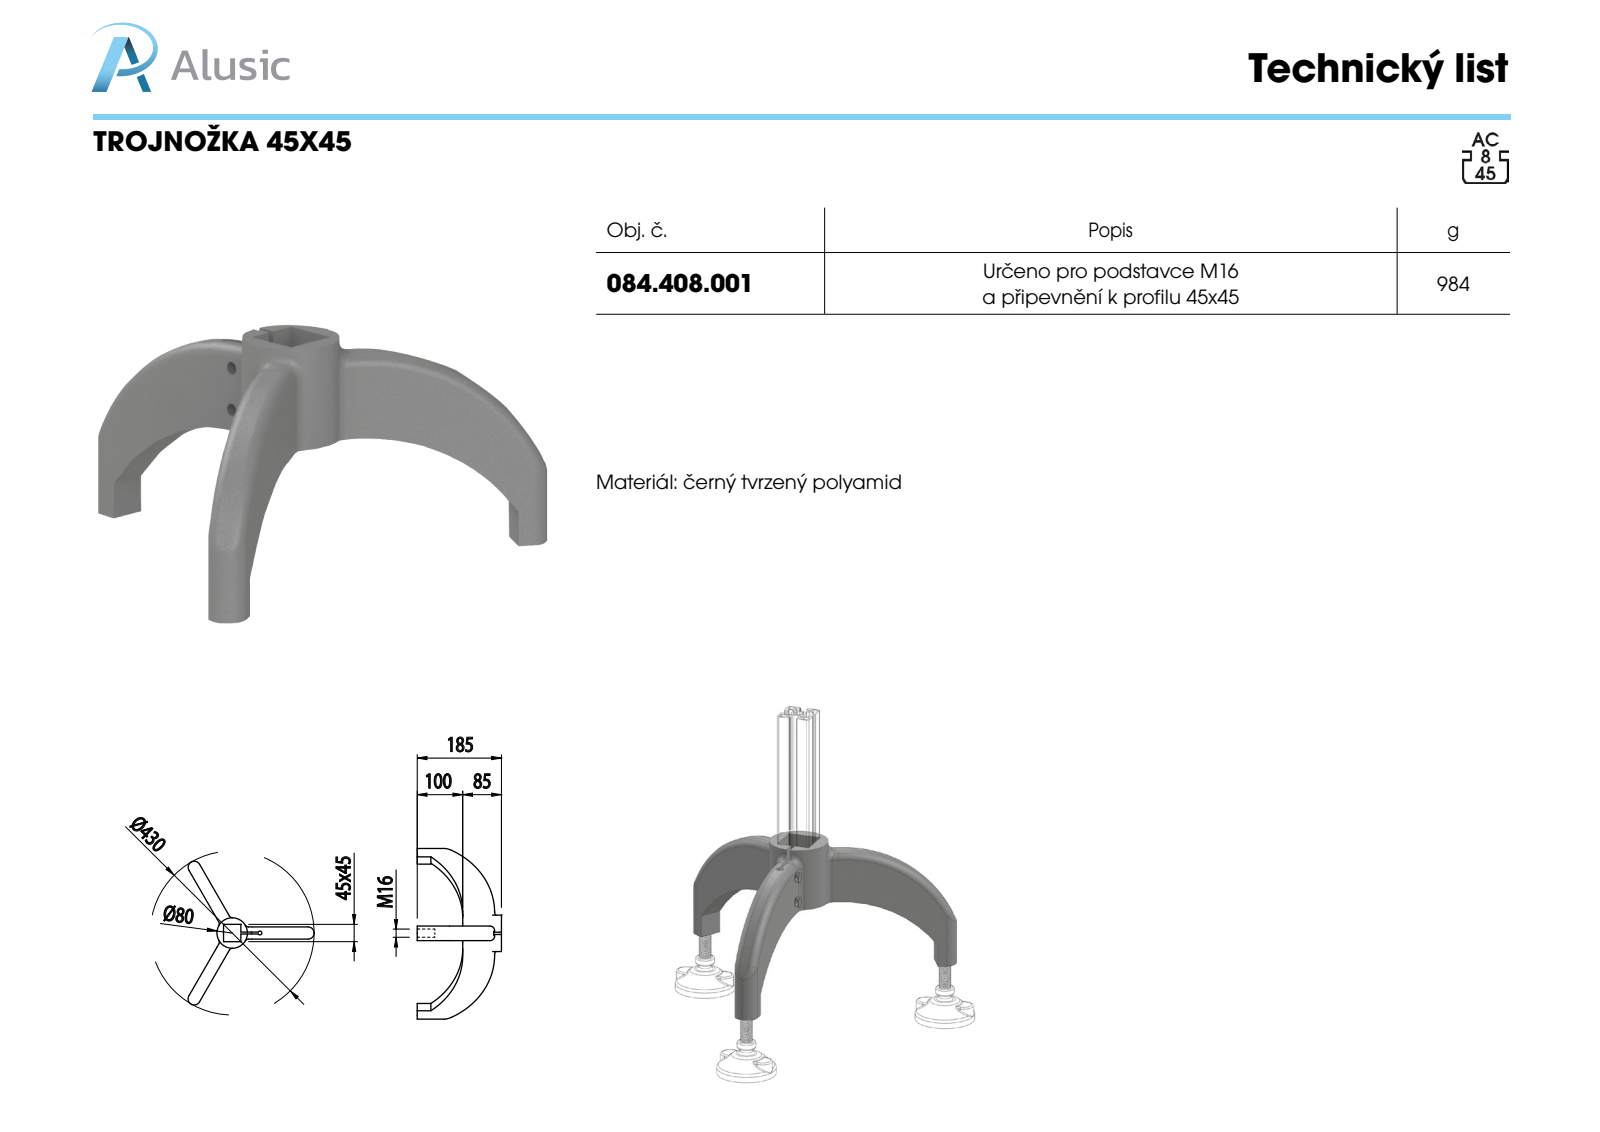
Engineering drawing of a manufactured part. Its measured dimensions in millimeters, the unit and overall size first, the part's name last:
Units: millimetres
Overall size (bounding box): 376.68 × 330.5 × 185
Round holes (diameter × count): ⌀14 ×3, ⌀10.5 ×2, ⌀10 ×1
Round bosses / shafts (diameter × count): ⌀80 ×1
Partial cylindrical surfaces — rounded edges, fillets, slot ends (radius × count): R10 ×12, R16 ×3, R173.01 ×3, R175.77 ×3
Main face-to-face distances: 32, 6.75, 38.75, 45.5, 20.25, 25.25, 13.5, 18.5, 5, 85
Hole centre spacings: 344.68, 243.66, 35, 126.25
Volume: 1 409 000 mm³ · Surface area: 171 630 mm²
Bodies: 1 solid, 98 faces (32 planar, 44 cylindrical, 22 other)
Part name (STEP PRODUCT): 084.408.001
STEP written by: SolidWorks 2011 (CONFIG_CONTROL_DESIGN)
